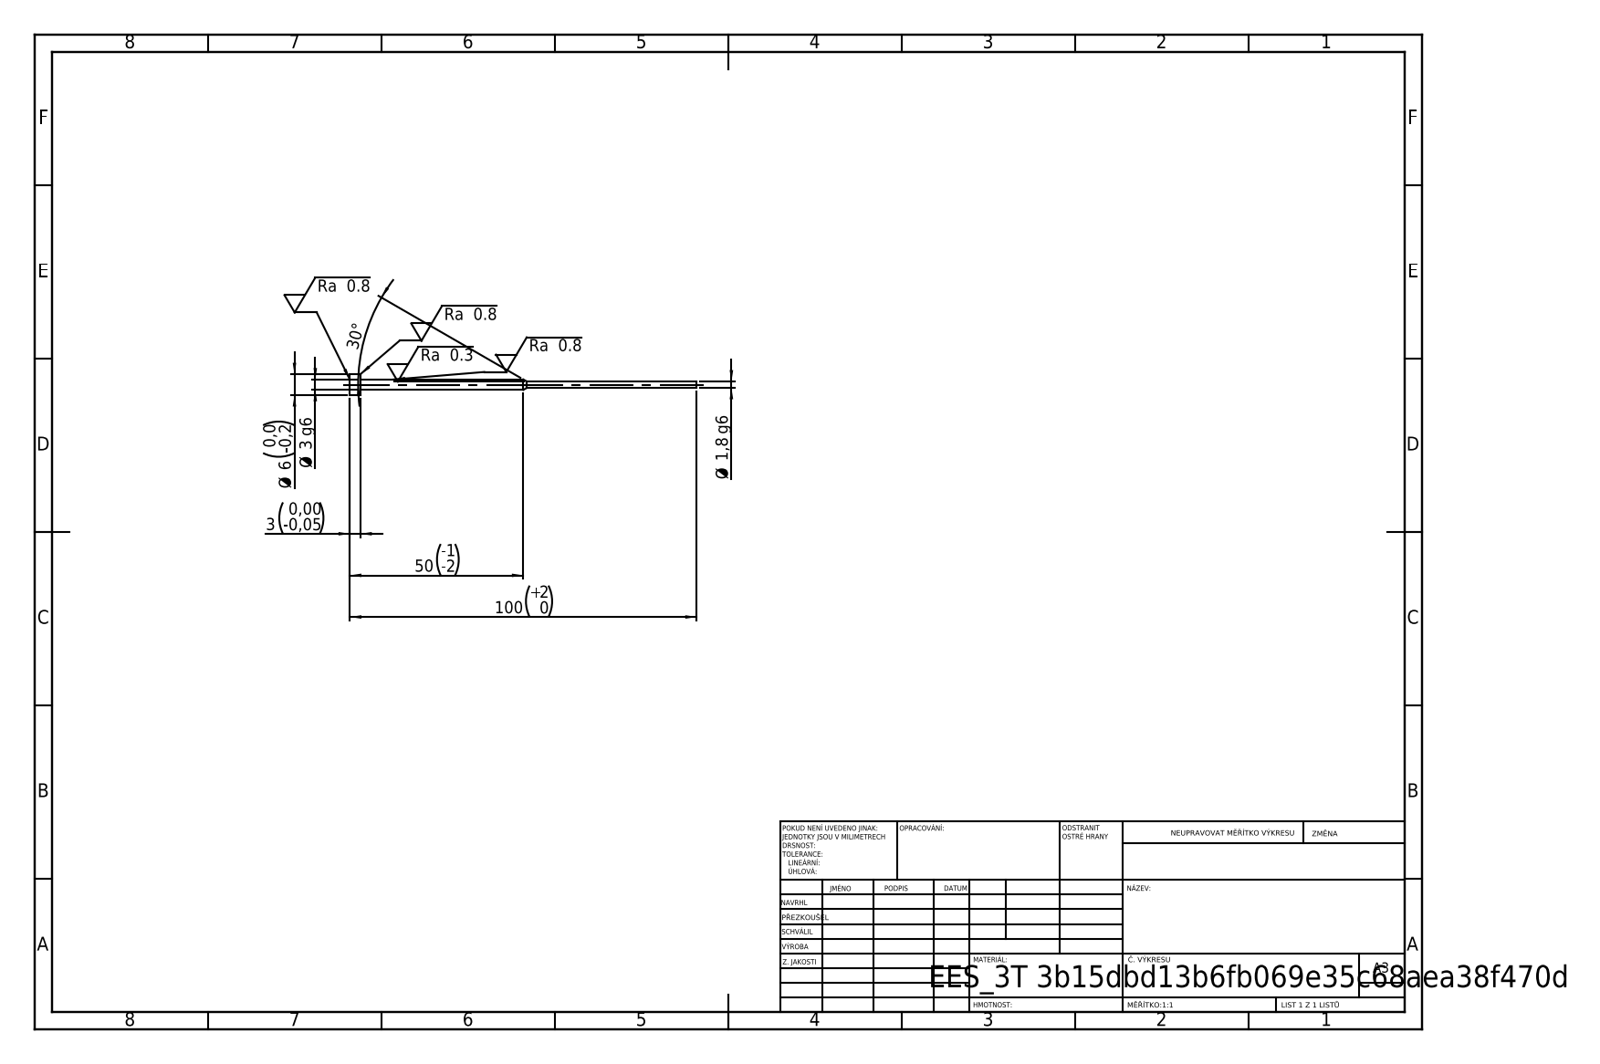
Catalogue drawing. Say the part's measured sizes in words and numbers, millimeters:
Its 3-D file was written by "SolidWorks 2019 (CONFIG_CONTROL_DESIGN)". It is 1 solid with 11 faces: 3 planar, 6 cylindrical and 2 other. Overall it measures 100 by 6 by 6 millimeters. Its volume is 546 cubic millimeters and its surface area 837 square millimeters. Round bosses or shafts: 1 of diameter 6, 1 of diameter 3, 1 of diameter 1.8. The main face-to-face distances are 3, 97, 100.
